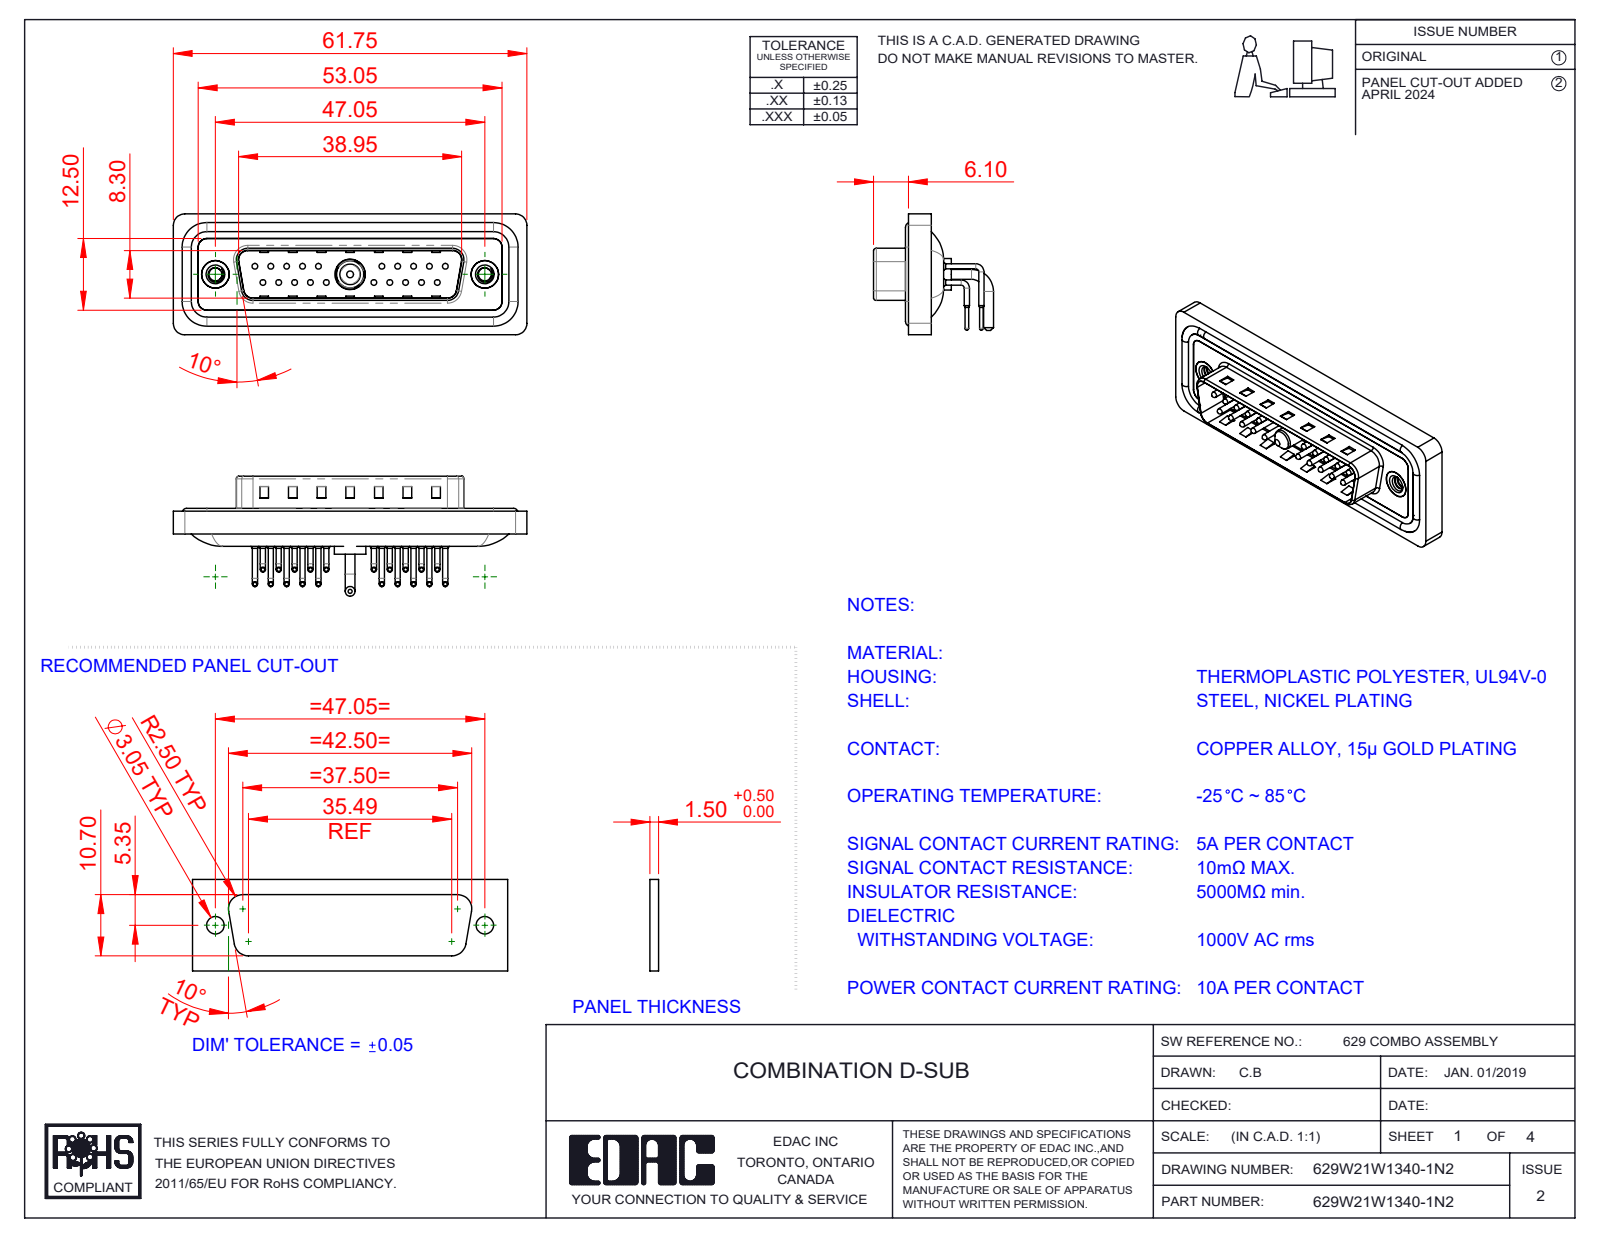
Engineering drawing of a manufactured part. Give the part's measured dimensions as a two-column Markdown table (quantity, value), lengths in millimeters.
| quantity | value |
| --- | --- |
| part name | 629Combo Threaded Rivet_2; 629W21W1340-1N2; 629Combo Housing_21W1; Power Pin_10A RA (+5 more) |
| STEP written by | SolidWorks 2023 (CONFIG_CONTROL_DESIGN) |
| units | millimeters |
| bodies | 29 solids, 2726 faces (1499 planar, 929 cylindrical, 298 other) |
| overall size | 61.75 × 21.1 × 20.95 |
| volume | 7 371 mm³ |
| surface area | 12 670 mm² |
| round holes (diameter × count) | 0.75 × 20, 1.6 × 20, 2 × 20, 2.26 × 2, 4 × 2, 4.8 × 2, 5 × 2, 4.85 × 1, 5.3 × 1 |
| round bosses / shafts (diameter × count) | 0.9 × 40, 1.5 × 20, 1 × 20, 0.65 × 20, 1.6 × 4, 4.9 × 2, 1.7 × 2, 5.5 × 1 |
| partial cylindrical surfaces (radius × count) | 1.01 × 20, 1.5 × 18, 2 × 18, 0.5 × 8, 1.6 × 8, 0.25 × 4, 0.6 × 4, 0.65 × 4 |
| main face-to-face distances | 0.4, 2.9, 0.8, 4.1, 1.1, 2.1, 1.6, 4.5, 1.5, 2.5 |
| hole center spacings | 3.16, 2.77, 5.54, 8.31, 5.04, 19.39, 20.97, 22.16 |
